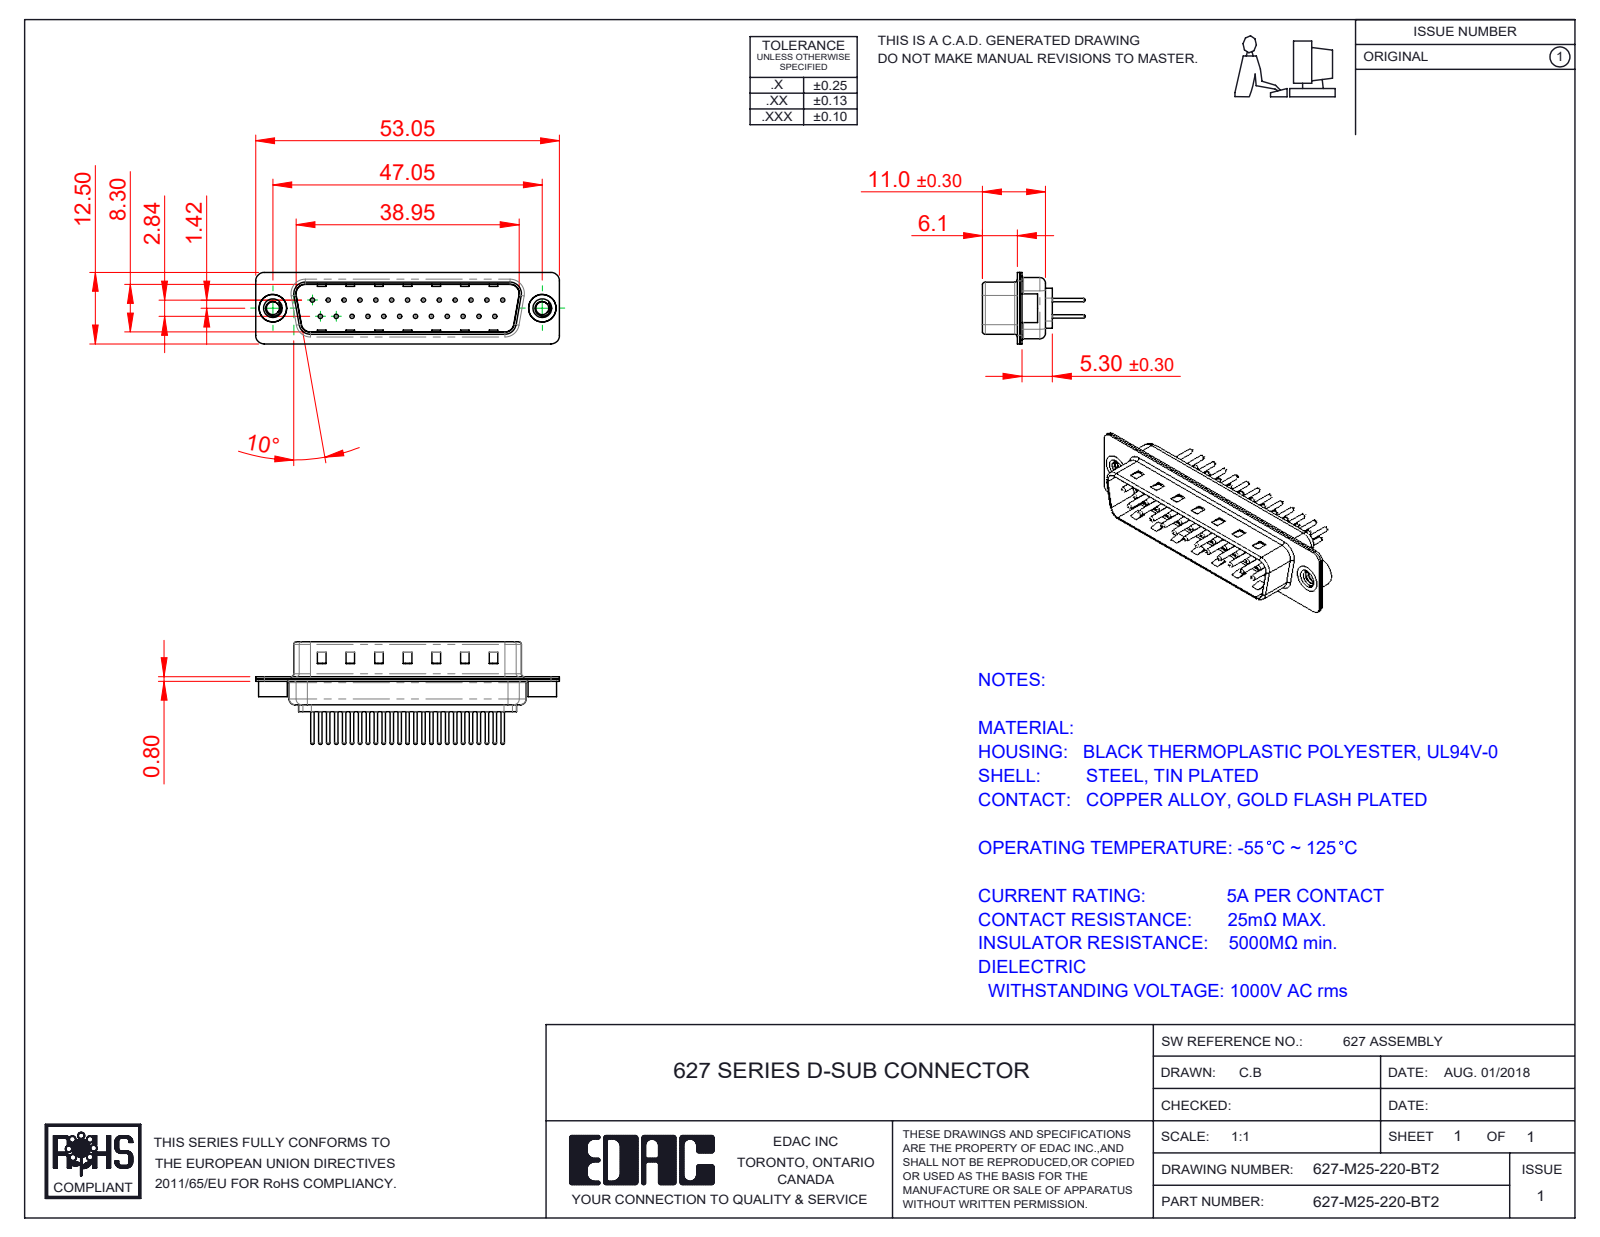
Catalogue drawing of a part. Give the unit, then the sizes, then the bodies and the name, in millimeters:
Units: millimetres
Overall size (bounding box): 53.05 × 17.9 × 12.5
Round holes (diameter × count): ⌀0.75 ×25, ⌀1.6 ×25, ⌀2 ×25, ⌀2.26 ×2, ⌀4 ×2, ⌀4.8 ×2
Round bosses / shafts (diameter × count): ⌀1.5 ×25, ⌀0.6 ×25, ⌀5 ×2, ⌀4.9 ×2
Partial cylindrical surfaces — rounded edges, fillets, slot ends (radius × count): R1.5 ×16, R2 ×12, R0.5 ×8, R1.6 ×8, R0.25 ×4, R0.6 ×4, R0.65 ×4, R0.9 ×4
Main face-to-face distances: 0.4, 0.8, 9.5, 9.1, 8.7, 9.9, 1.2, 6.1, 5.7, 0.75
Hole centre spacings: 3.16, 2.77, 5.54, 8.31, 11.08, 13.85, 16.62, 5.03
Volume: 2 719 mm³ · Surface area: 6 843 mm²
Bodies: 30 solids, 1301 faces (346 planar, 487 cylindrical, 468 other)
Part name (STEP PRODUCT): 627M Contact Row 2_20; 627M Shell Front_25 Contacts; 627-M25-220-BT2; 627M Shell Rear_25 Contacts (+3 more)
STEP written by: SolidWorks 2020 (CONFIG_CONTROL_DESIGN)
